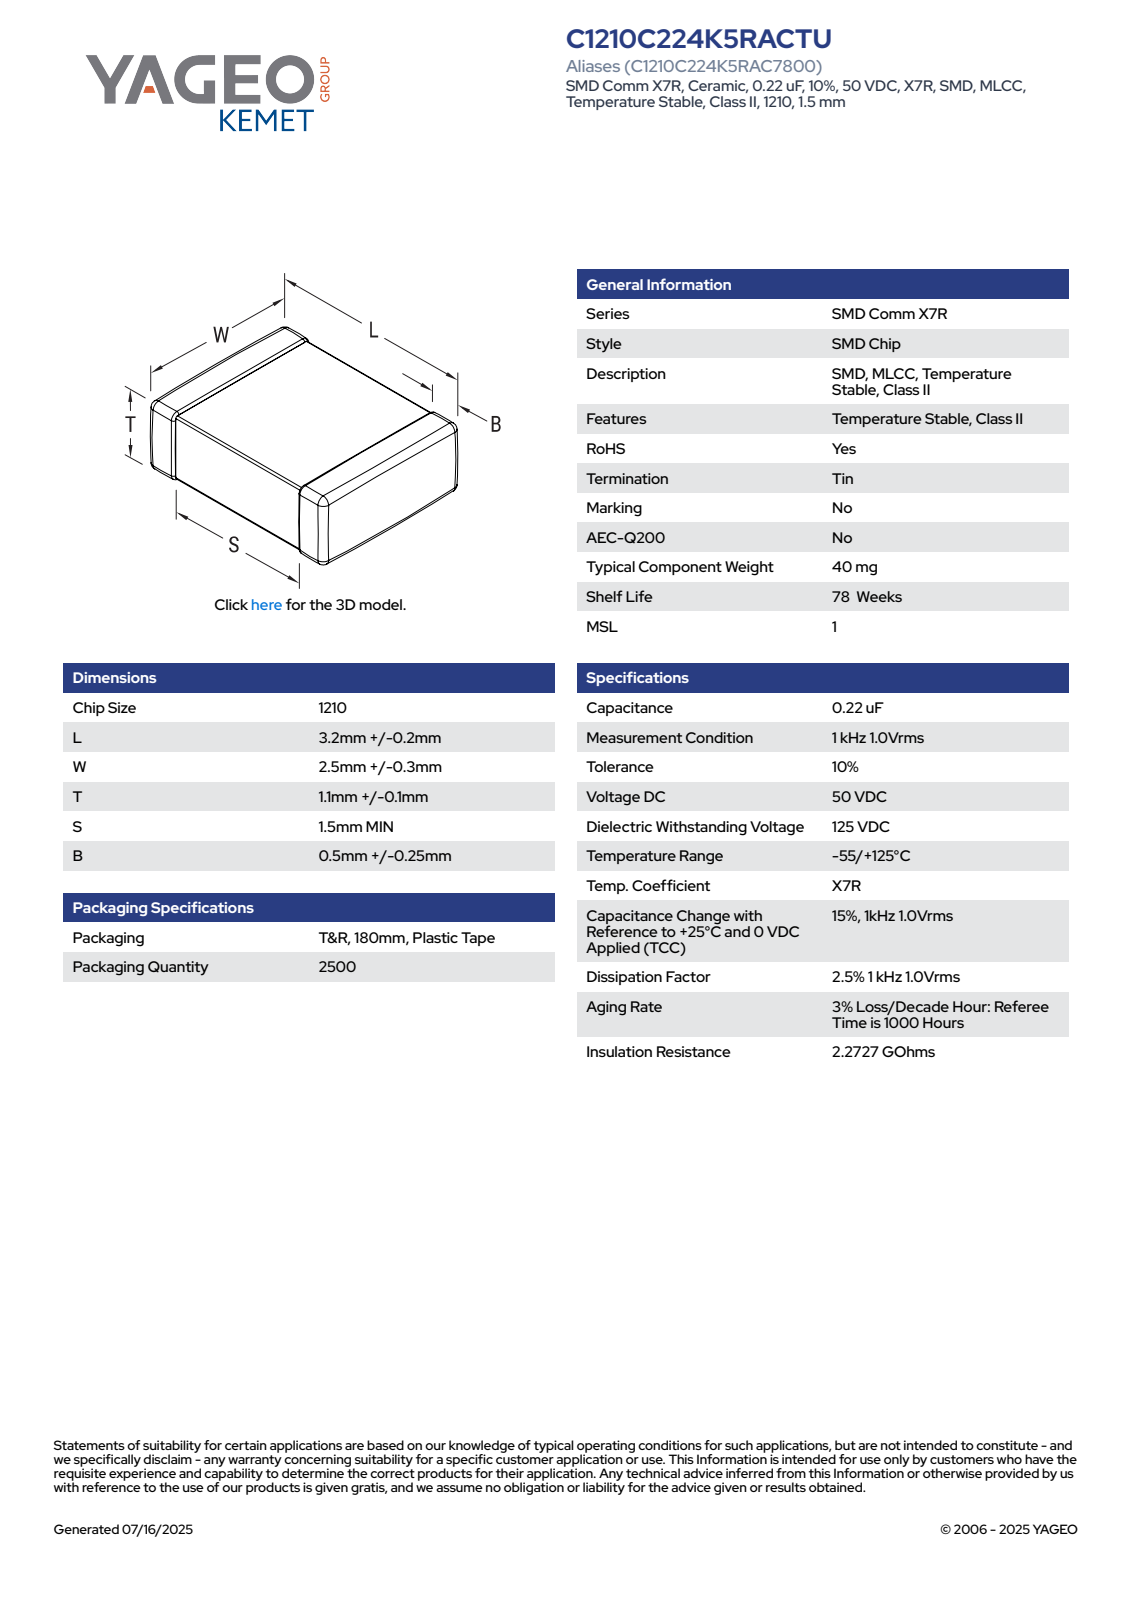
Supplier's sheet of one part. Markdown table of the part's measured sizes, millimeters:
| quantity | value |
| --- | --- |
| part name | CCS_CCSTD_1210_L3.4W2.8T1.2B0.5 |
| STEP written by | SolidWorks 2021 (AUTOMOTIVE_DESIGN) |
| units | millimeters |
| bodies | 4 solids, 125 faces (71 planar, 38 cylindrical, 16 other) |
| overall size | 3.4 × 2.8 × 1.2 |
| volume | 11 mm³ |
| surface area | 34 mm² |
| main face-to-face distances | 1.14, 1.08, 1.2, 3.4, 2.74, 2.68, 2.8, 1.15, 1.09, 0.42 |
